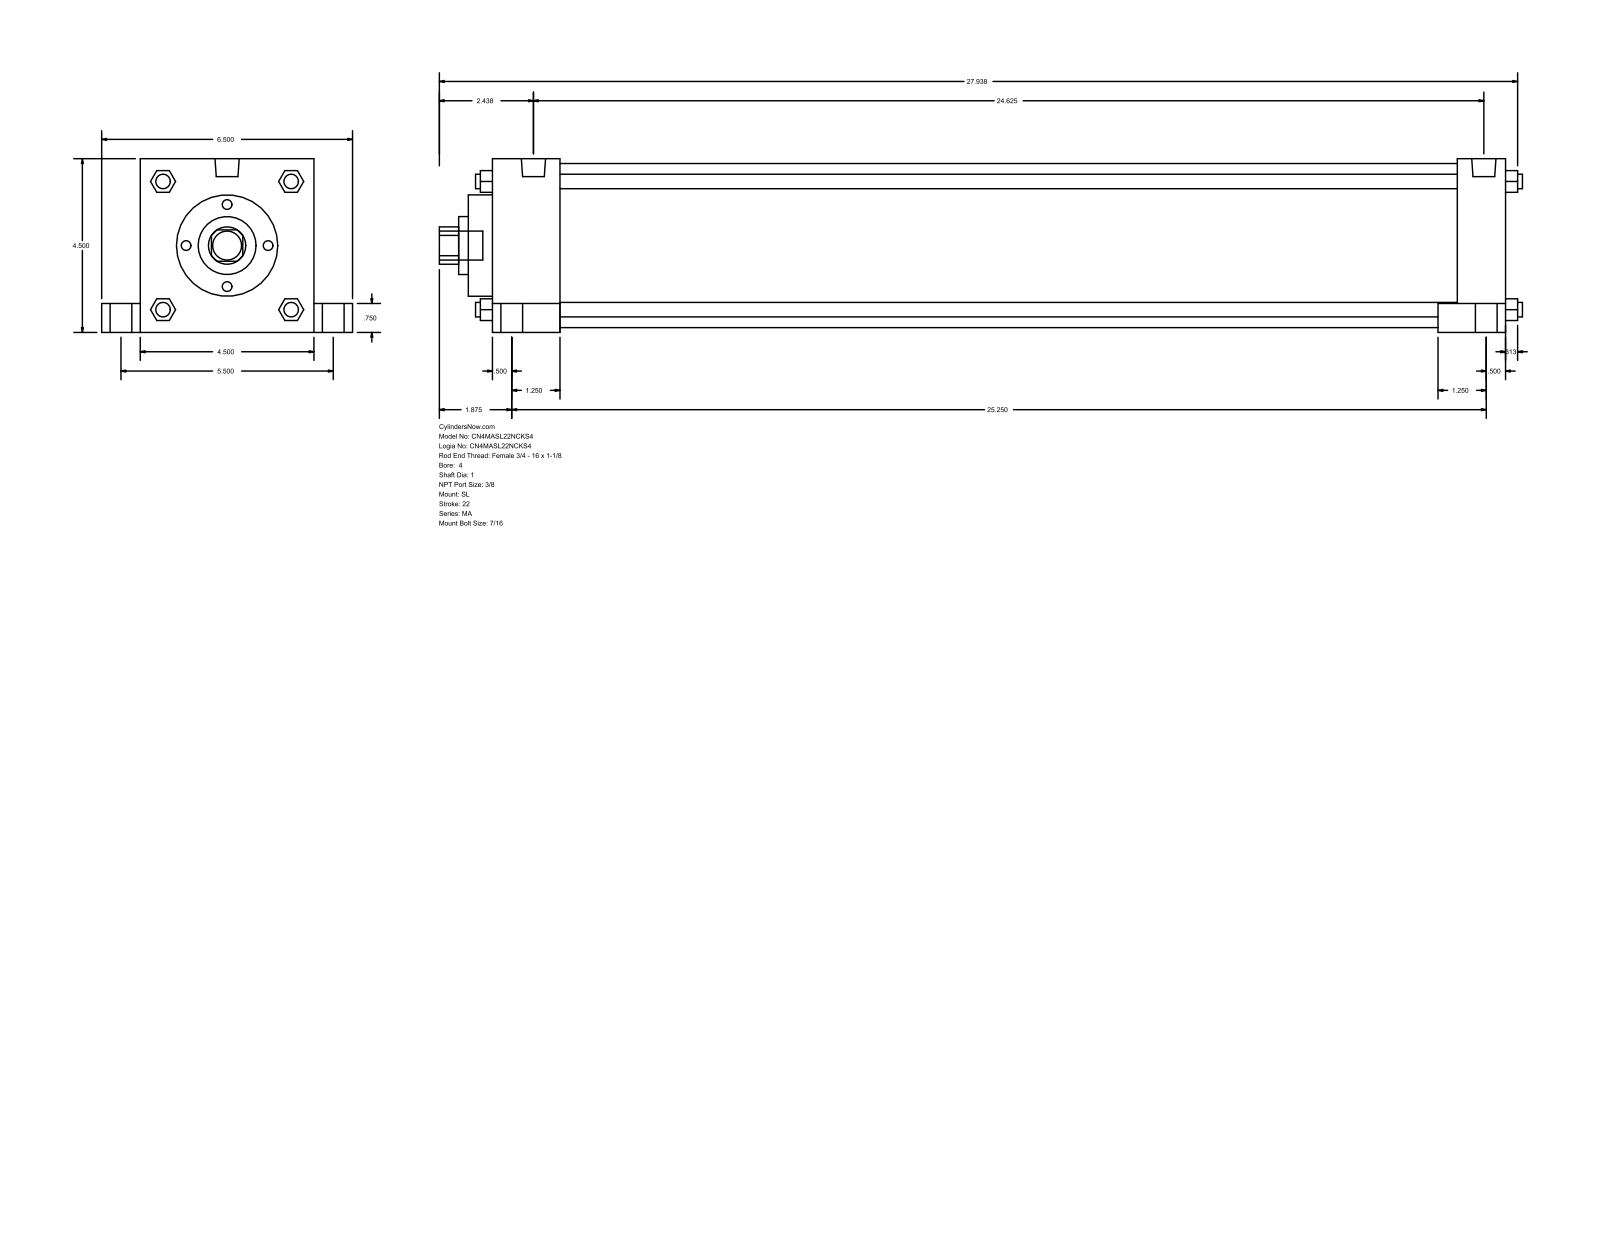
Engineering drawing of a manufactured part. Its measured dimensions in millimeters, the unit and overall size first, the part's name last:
Units: millimetres
Overall size (bounding box): 712.79 × 165.1 × 114.3
Round holes (diameter × count): ⌀25.4 ×1, ⌀38.1 ×1, ⌀66.67 ×1, ⌀107.95 ×1
Round bosses / shafts (diameter × count): ⌀20.64 ×4, ⌀14.29 ×4, ⌀11.11 ×4, ⌀9.53 ×4, ⌀15.93 ×2, ⌀19.05 ×1
Partial cylindrical surfaces — rounded edges, fillets, slot ends (radius × count): R12.29 ×1
Main face-to-face distances: 114.3, 666.75, 44.46, 622.29, 635, 590.54, 31.75, 25.4, 139.7, 682.62
Bodies: 0 solids, 150 faces (113 planar, 37 cylindrical, 0 other)
Part name (STEP PRODUCT): MA_SL__0400_1
STEP written by: GSSL Pune (CONFIG_CONTROL_DESIGN)
